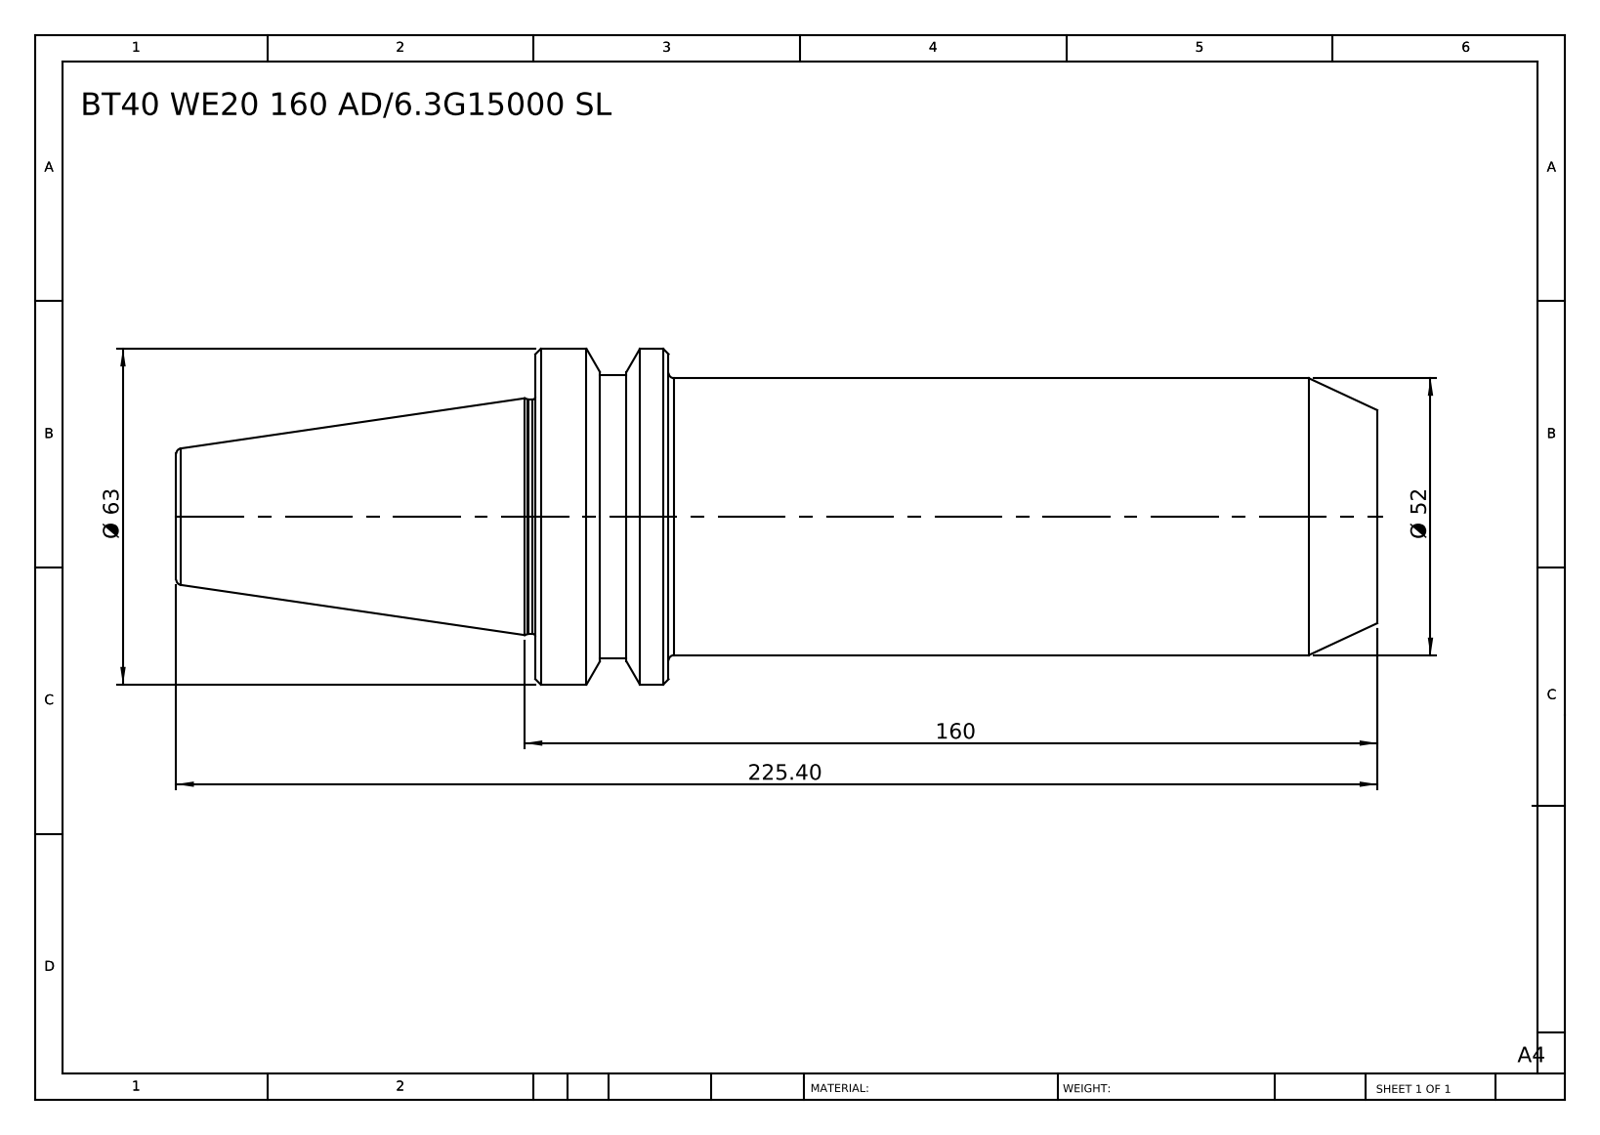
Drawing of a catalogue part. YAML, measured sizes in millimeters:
part_name: "BT40 WE20 160 AD-6.3G15000 SL"
step_written_by: "SolidWorks 2014 (CONFIG_CONTROL_DESIGN)"
units: millimeters
bodies: {solids: 1, faces: 38, planar: 6, cylindrical: 10, other: 22}
overall_size: [225.4, 63, 63]
volume: 415016
surface_area: 39073
round_bosses_or_shafts:
  - {diameter: 63, count: 1}
  - {diameter: 53, count: 1}
  - {diameter: 52, count: 1}
  - {diameter: 44, count: 1}
face_to_face_distances: [158, 133, 25, 225.4, 92.4, 67.4, 145.9, 12.9, 12.1, 79.5]
